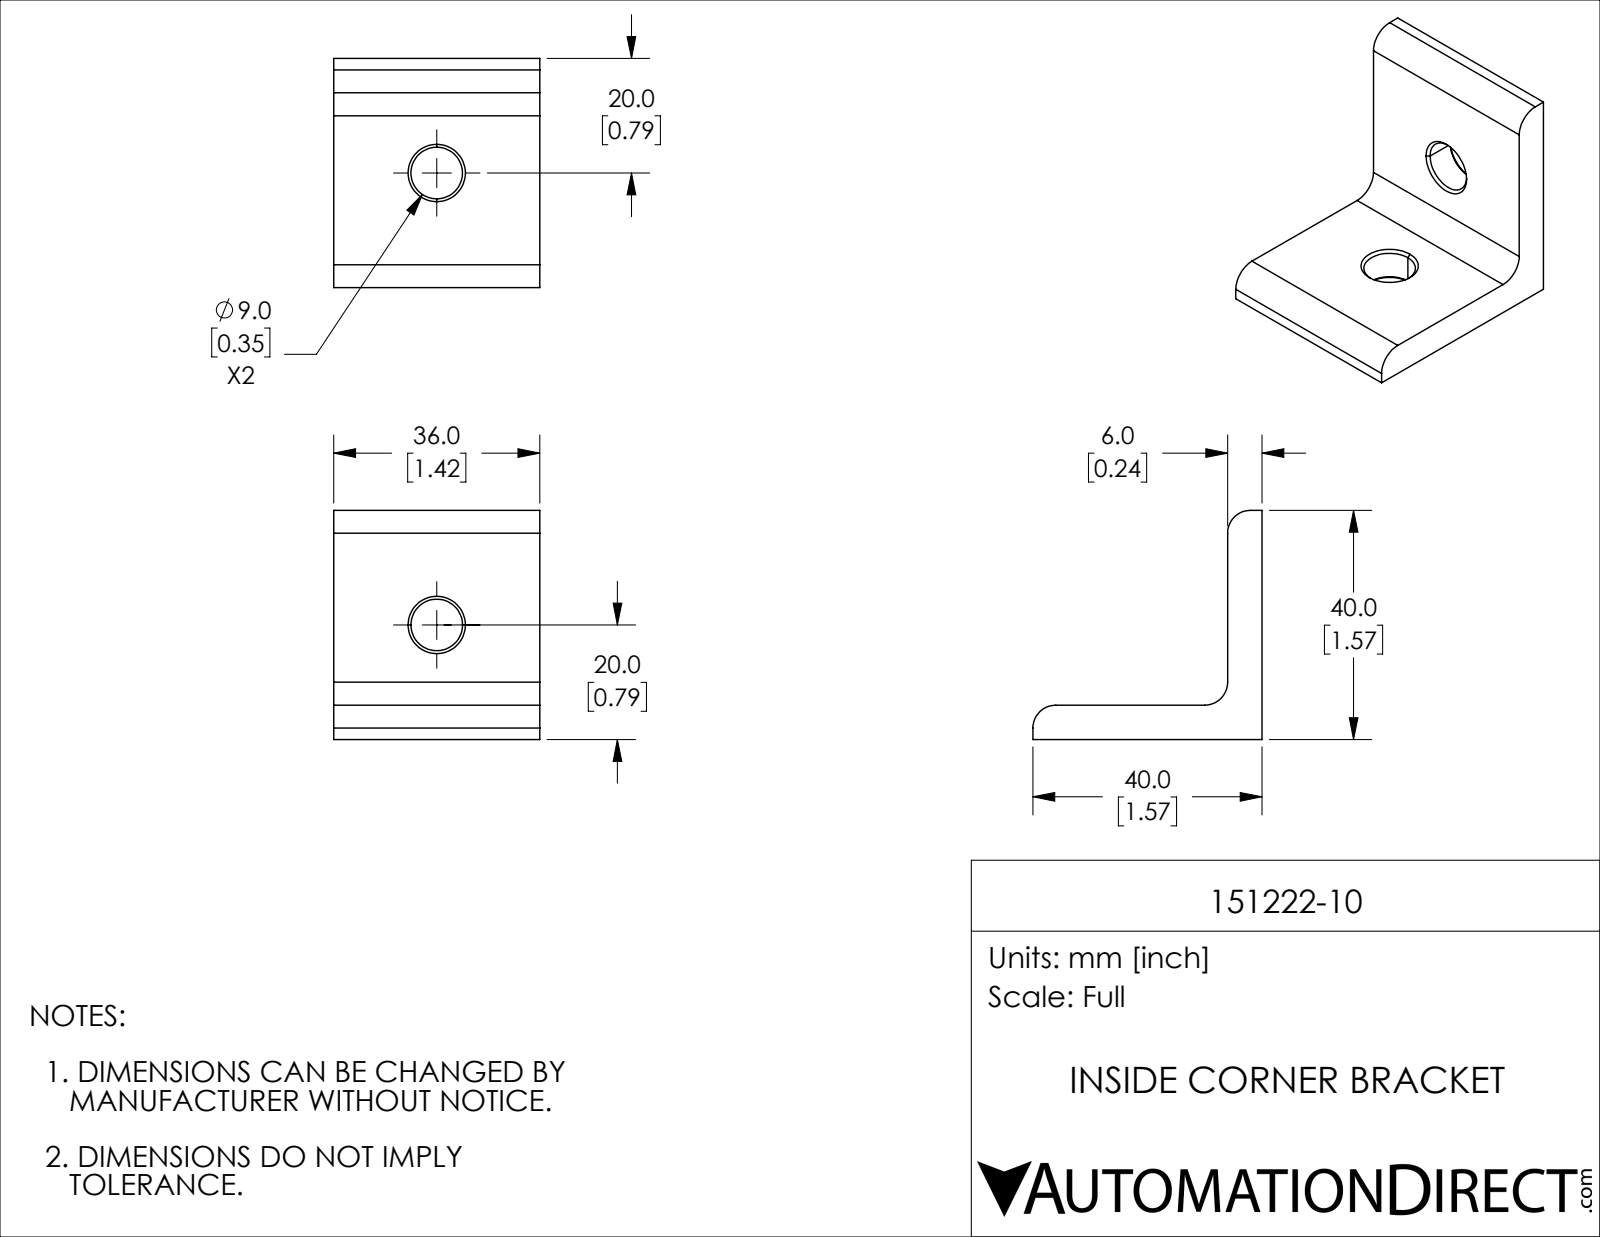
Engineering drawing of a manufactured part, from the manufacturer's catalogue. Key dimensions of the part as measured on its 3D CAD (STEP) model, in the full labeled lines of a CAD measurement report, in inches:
Part name (STEP PRODUCT): 151222-10
STEP written by: SolidWorks 2024 (CONFIG_CONTROL_DESIGN)
Units: inches
Bodies: 1 solid, 23 faces (8 planar, 7 cylindrical, 8 other)
Overall size (bounding box): 1.575 × 1.575 × 1.417
Volume: 0.92 in³ · Surface area: 10.09 in²
Round holes (diameter × count): ⌀0.354 ×2
Partial cylindrical surfaces — rounded edges, fillets, slot ends (radius × count): R0.157 ×3
Main face-to-face distances: 0.236, 1.417, 1.575, 1.339
